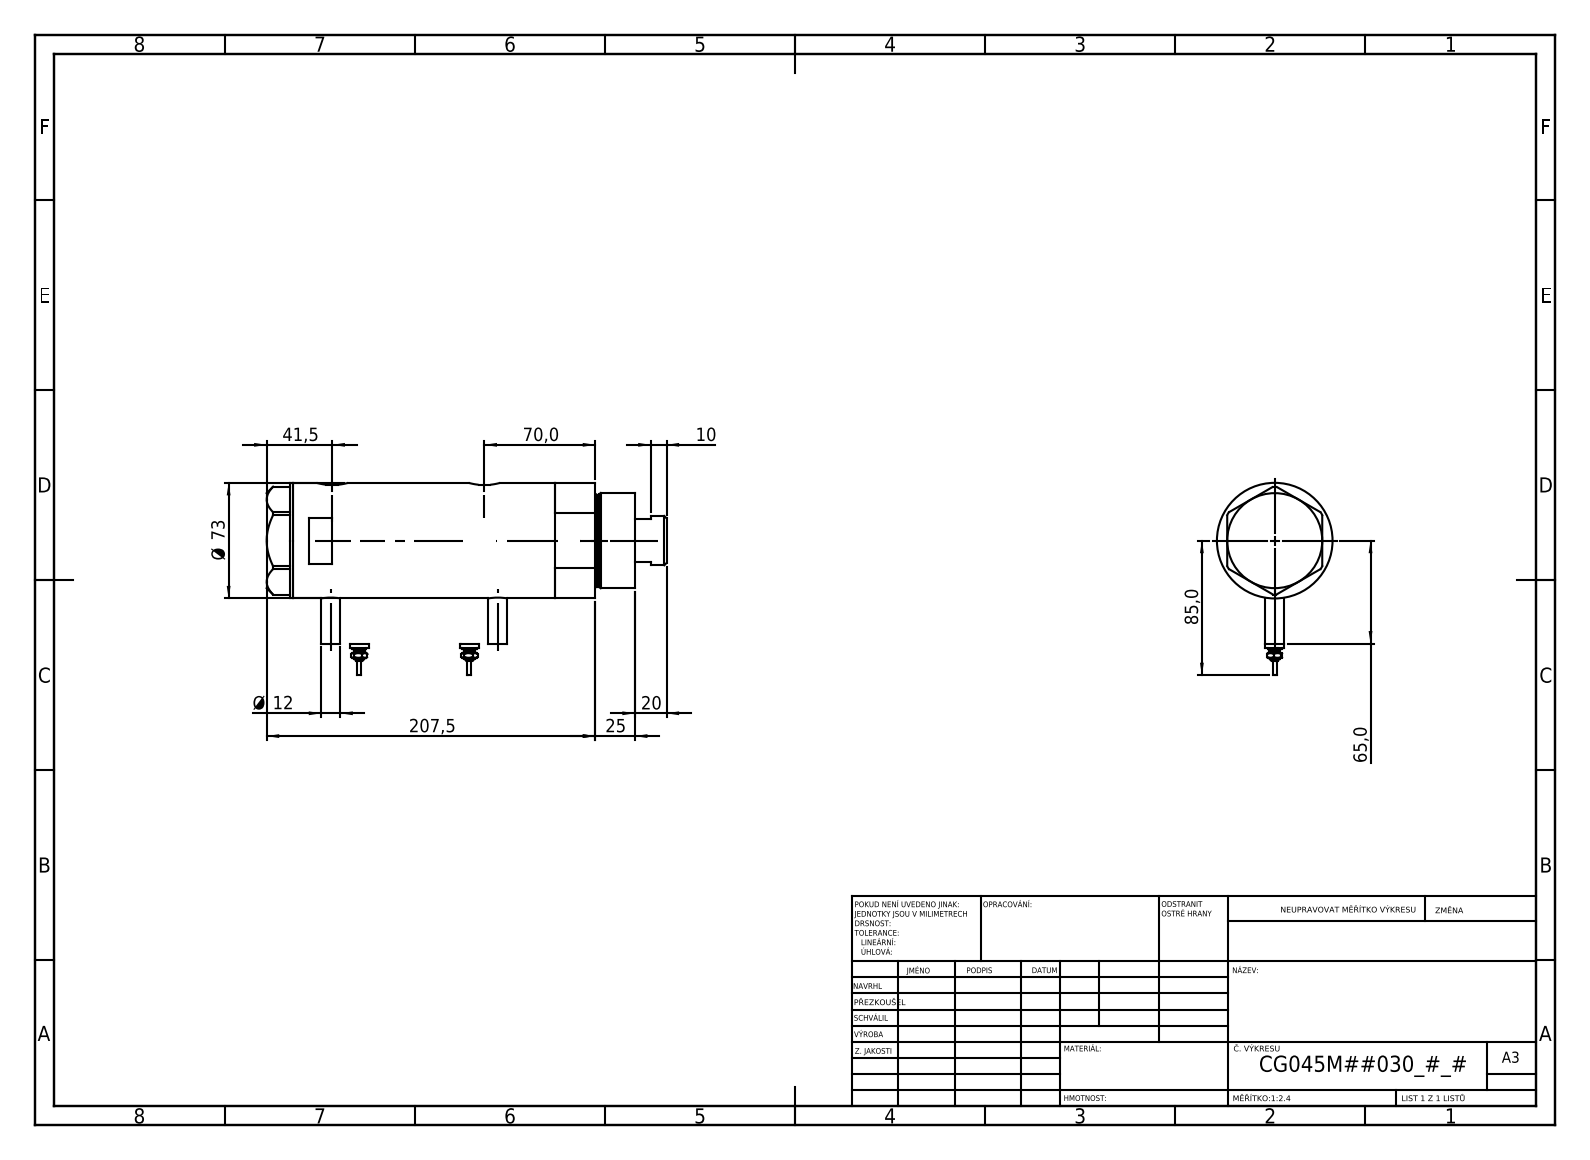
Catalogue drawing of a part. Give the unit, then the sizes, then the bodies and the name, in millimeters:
Units: millimetres
Overall size (bounding box): 252.5 × 121.5 × 73
Round holes (diameter × count): ⌀12.5 ×2, ⌀13.16 ×2, ⌀10.5 ×1, ⌀32 ×1, ⌀33.5 ×1, ⌀45 ×1, ⌀48 ×1, ⌀64 ×1
Round bosses / shafts (diameter × count): ⌀12 ×4, ⌀9 ×2, ⌀7 ×2, ⌀4.5 ×2, ⌀2.5 ×2, ⌀73 ×1, ⌀60 ×1, ⌀58 ×1
Partial cylindrical surfaces — rounded edges, fillets, slot ends (radius × count): R10 ×2
Main face-to-face distances: 95, 121, 26, 16.5, 42.5, 137.5, 2, 216, 232.5, 190
Hole centre spacings: 1, 8.5, 96, 97, 104.5, 105.5
Volume: 907 883 mm³ · Surface area: 152 546 mm²
Bodies: 6 solids, 212 faces (77 planar, 71 cylindrical, 64 other)
Part name (STEP PRODUCT): V270CG_BACK; V270CG_VC; Switch; V270CG_MIDDLE (+1 more)
STEP written by: SolidWorks 2019 (CONFIG_CONTROL_DESIGN)
